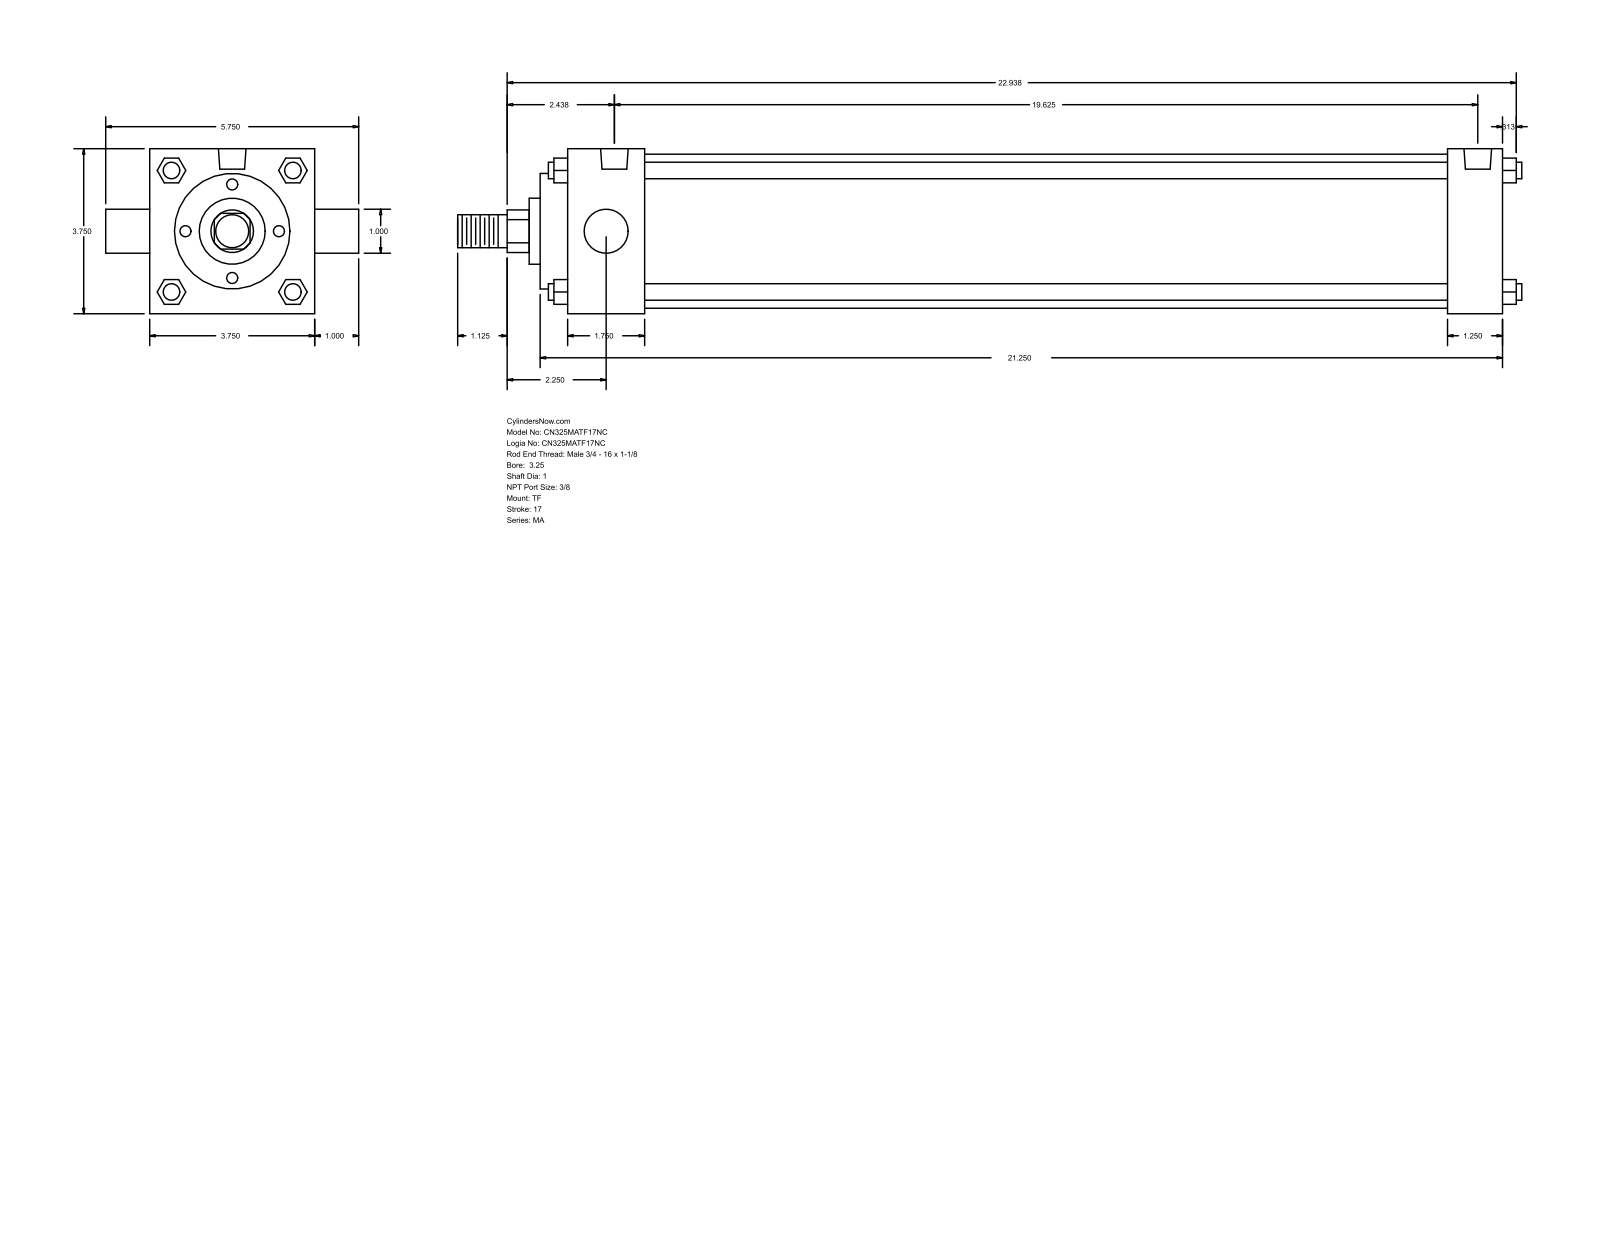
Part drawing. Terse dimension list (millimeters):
name: MA_TF__0325_1
written by: GSSL Pune (CONFIG_CONTROL_DESIGN)
unit: mm
bodies: 0 solids, 122 faces (93 planar, 29 cylindrical, 0 other)
size: 614.36 × 146.05 × 95.25
holes: 3× ⌀11.11, 2× ⌀15.93
bosses: 4× ⌀9.53, 2× ⌀25.4, 1× ⌀88.9, 1× ⌀66.67, 1× ⌀38.1, 1× ⌀19.05
rounds: 1× R12.29
face distances: 95.24, 539.75, 555.62, 44.46, 508, 463.54, 495.29, 31.75, 15.87, 60.33
hole spacings: 4.76, 4.77, 488.95, 493.71, 493.72, 498.48
